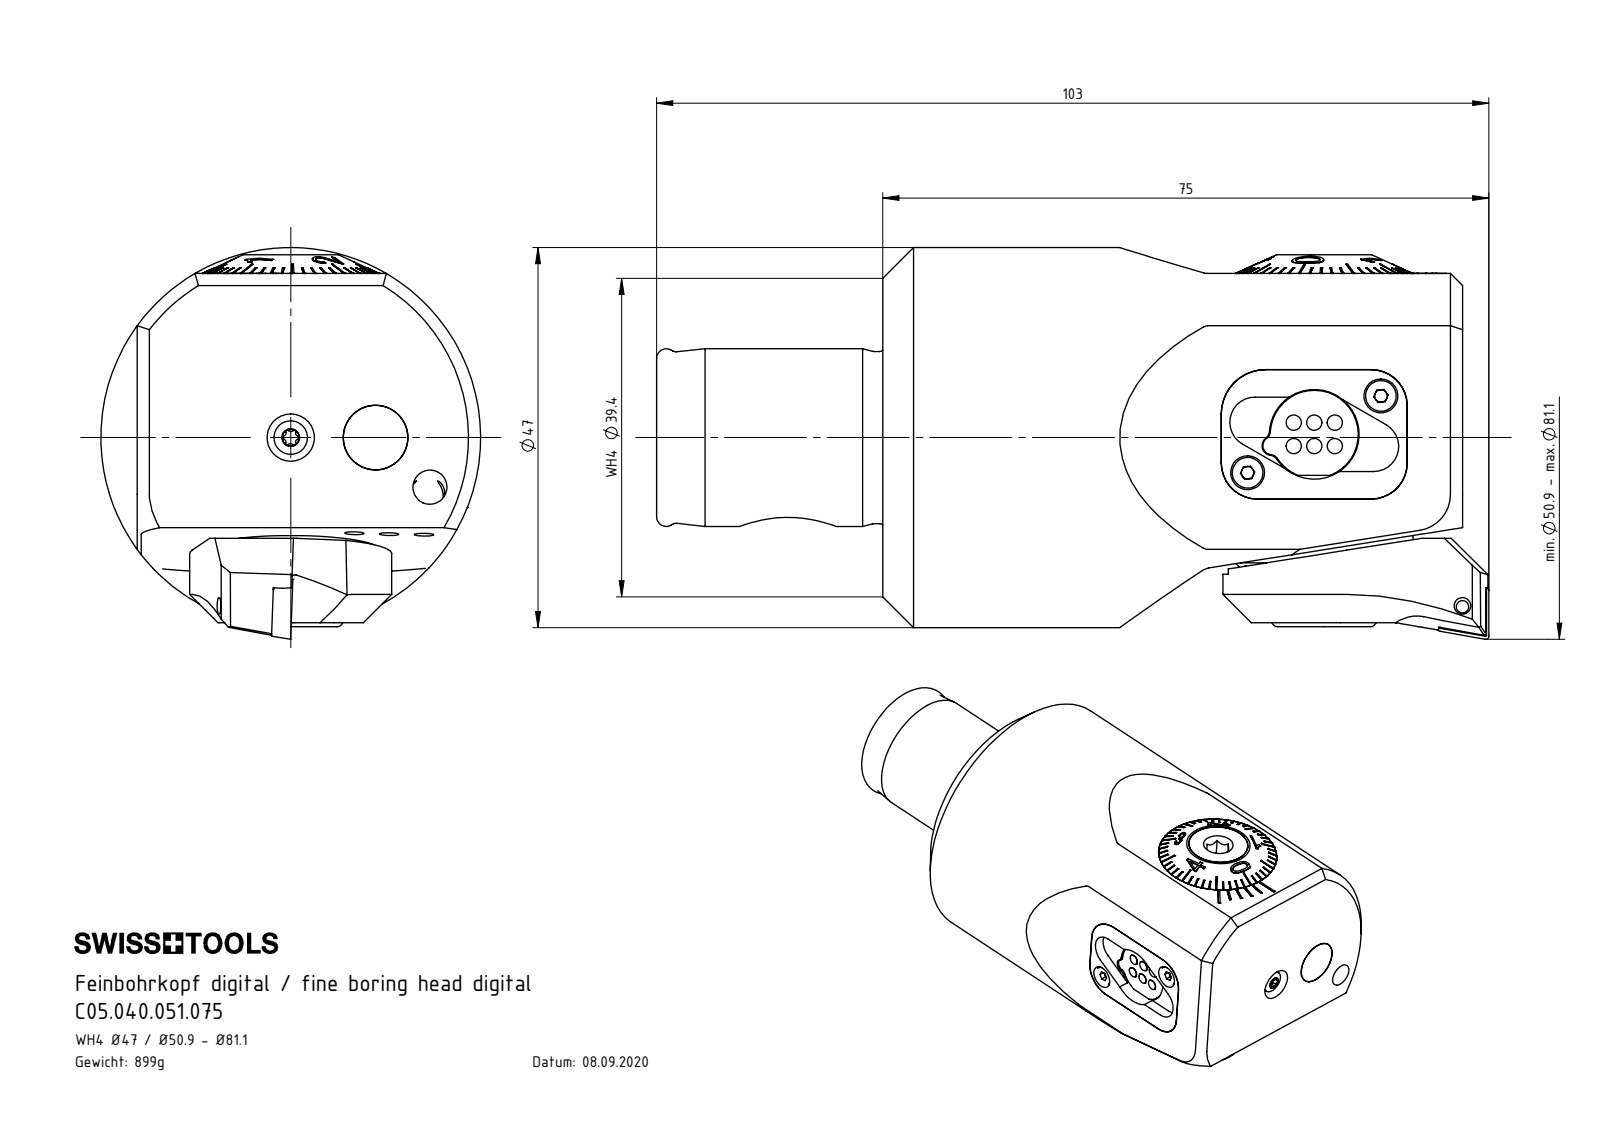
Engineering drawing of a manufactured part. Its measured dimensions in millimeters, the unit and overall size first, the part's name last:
Units: millimetres
Overall size (bounding box): 103 × 45.8 × 42
Round holes (diameter × count): ⌀3.3 ×4, ⌀6.8 ×3, ⌀1.6 ×2, ⌀2.2 ×2, ⌀2.5 ×2, ⌀4.2 ×2, ⌀2.05 ×1, ⌀2.1 ×1, ⌀2.8 ×1, ⌀3 ×1, ⌀3.2 ×1, ⌀3.85 ×1
Round bosses / shafts (diameter × count): ⌀1.9 ×6, ⌀8 ×2, ⌀3.8 ×2, ⌀2 ×2, ⌀42 ×1, ⌀40 ×1, ⌀22 ×1, ⌀21.98 ×1
Partial cylindrical surfaces — rounded edges, fillets, slot ends (radius × count): R0.21 ×12, R0.36 ×10, R1.2 ×8, R1.1 ×6, R0.5 ×5, R3.2 ×5, R4.5 ×4, R4.4 ×3
Main face-to-face distances: 71.75, 27.7, 4.5, 4, 5.6, 34.7, 2.3, 1.1, 2, 2.2
Hole centre spacings: 9.52, 3.84, 3.99, 7.67, 10.5, 15.58, 19.04, 24.85
Volume: 100 372 mm³ · Surface area: 33 093 mm²
Bodies: 25 solids, 1038 faces (436 planar, 251 cylindrical, 351 other)
Part name (STEP PRODUCT): ISO 4762 - M2 x 6; Fxx-MAB.xxx.xxx_A_F42; PEF-DA1.011.017_A; F42-WCA.001.009_C_fertigbearbeitet (+8 more)
STEP written by: SolidWorks 2015 (AUTOMOTIVE_DESIGN)
